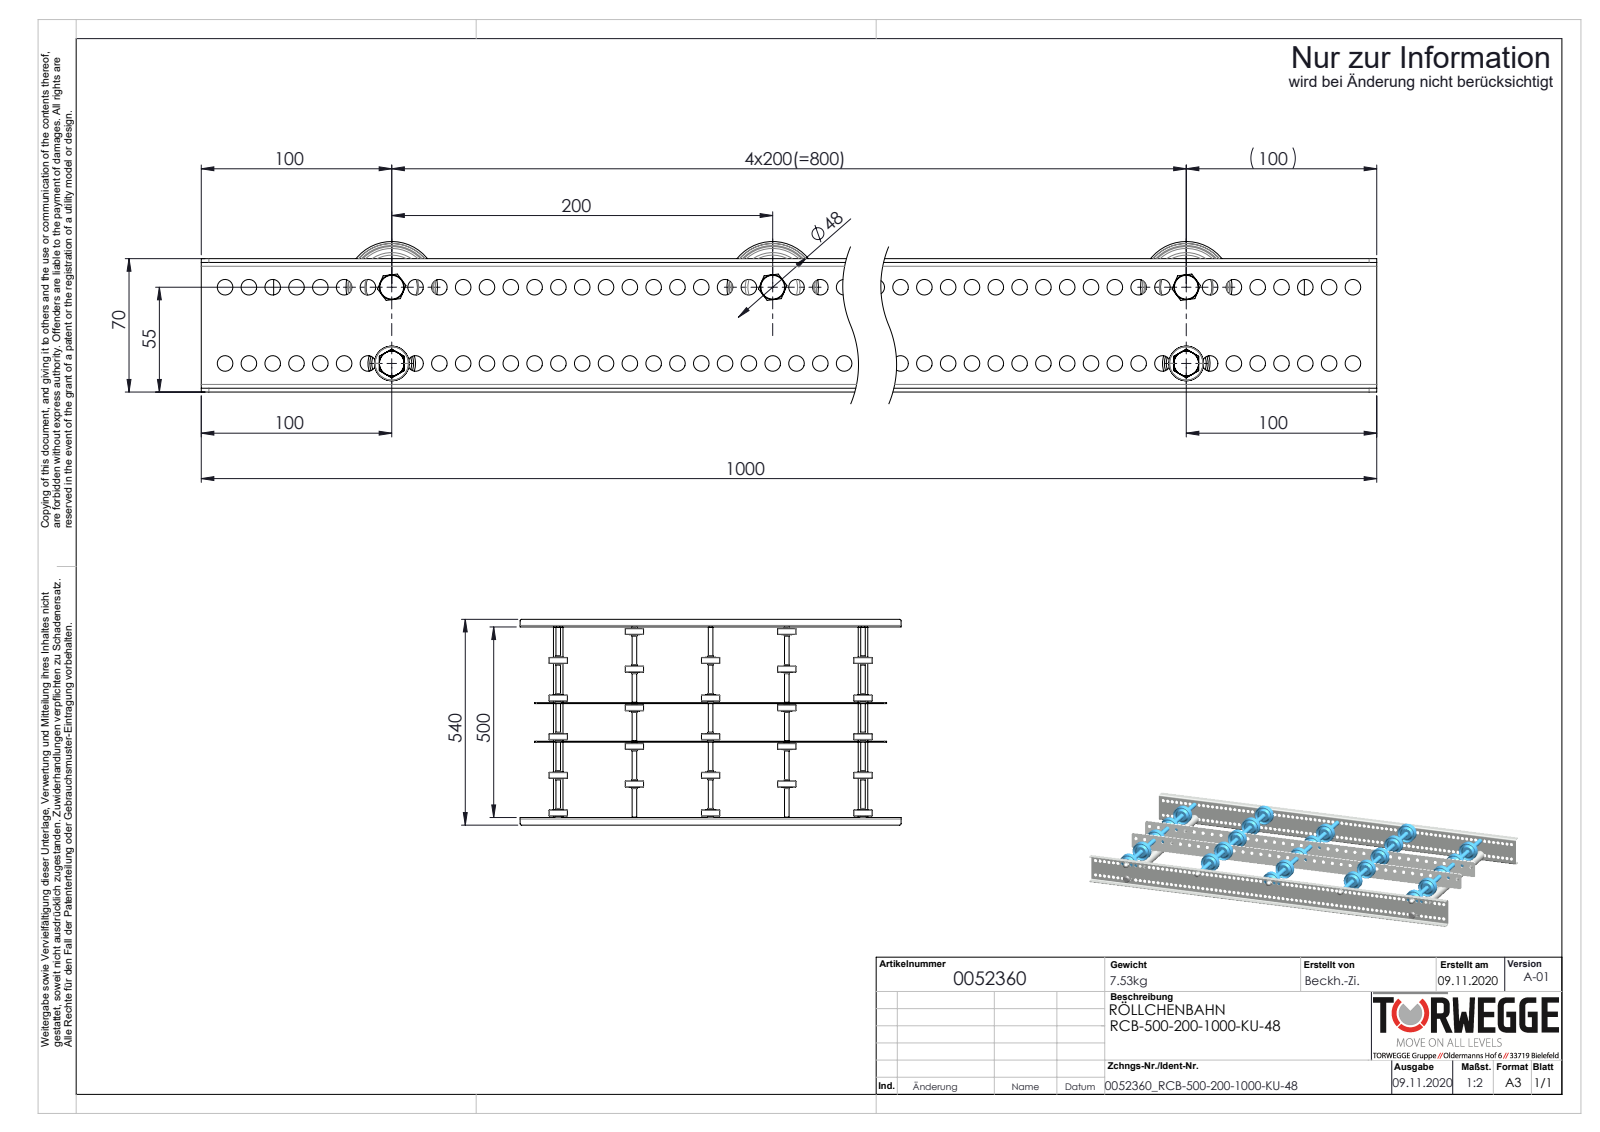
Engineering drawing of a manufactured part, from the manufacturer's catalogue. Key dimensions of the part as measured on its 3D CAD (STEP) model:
Part name (STEP PRODUCT): 0052360; Hutmutter_DIN_1587_M8; 0011532_2300-48-8; S100100_Längstraverse-42x2,5_S100101_Lngstraverse-RB-L975 (+6 more)
STEP written by: SolidWorks 2020 (AUTOMOTIVE_DESIGN)
Units: millimetres
Bodies: 79 solids, 3275 faces (547 planar, 1444 cylindrical, 1284 other)
Overall size (bounding box): 1000 × 540 × 79
Volume: 1 426 000 mm³ · Surface area: 1 167 000 mm²
Round holes (diameter × count): ⌀8.2 ×158, ⌀8.5 ×37, ⌀6.65 ×5, ⌀9.65 ×5, ⌀13.7 ×5, ⌀6.8 ×2, ⌀21 ×2
Round bosses / shafts (diameter × count): ⌀8 ×7, ⌀48 ×5, ⌀27 ×5, ⌀12.7 ×5, ⌀12.5 ×5, ⌀12 ×5, ⌀25 ×2
Partial cylindrical surfaces — rounded edges, fillets, slot ends (radius × count): R4 ×8, R2 ×4, R5 ×4
Main face-to-face distances: 2, 502, 101.3, 2.5, 68, 504, 500, 200.1, 301.4, 98.8
Hole centre spacings: 12.5, 25, 37.5, 50, 62.5, 75, 87.5, 100
